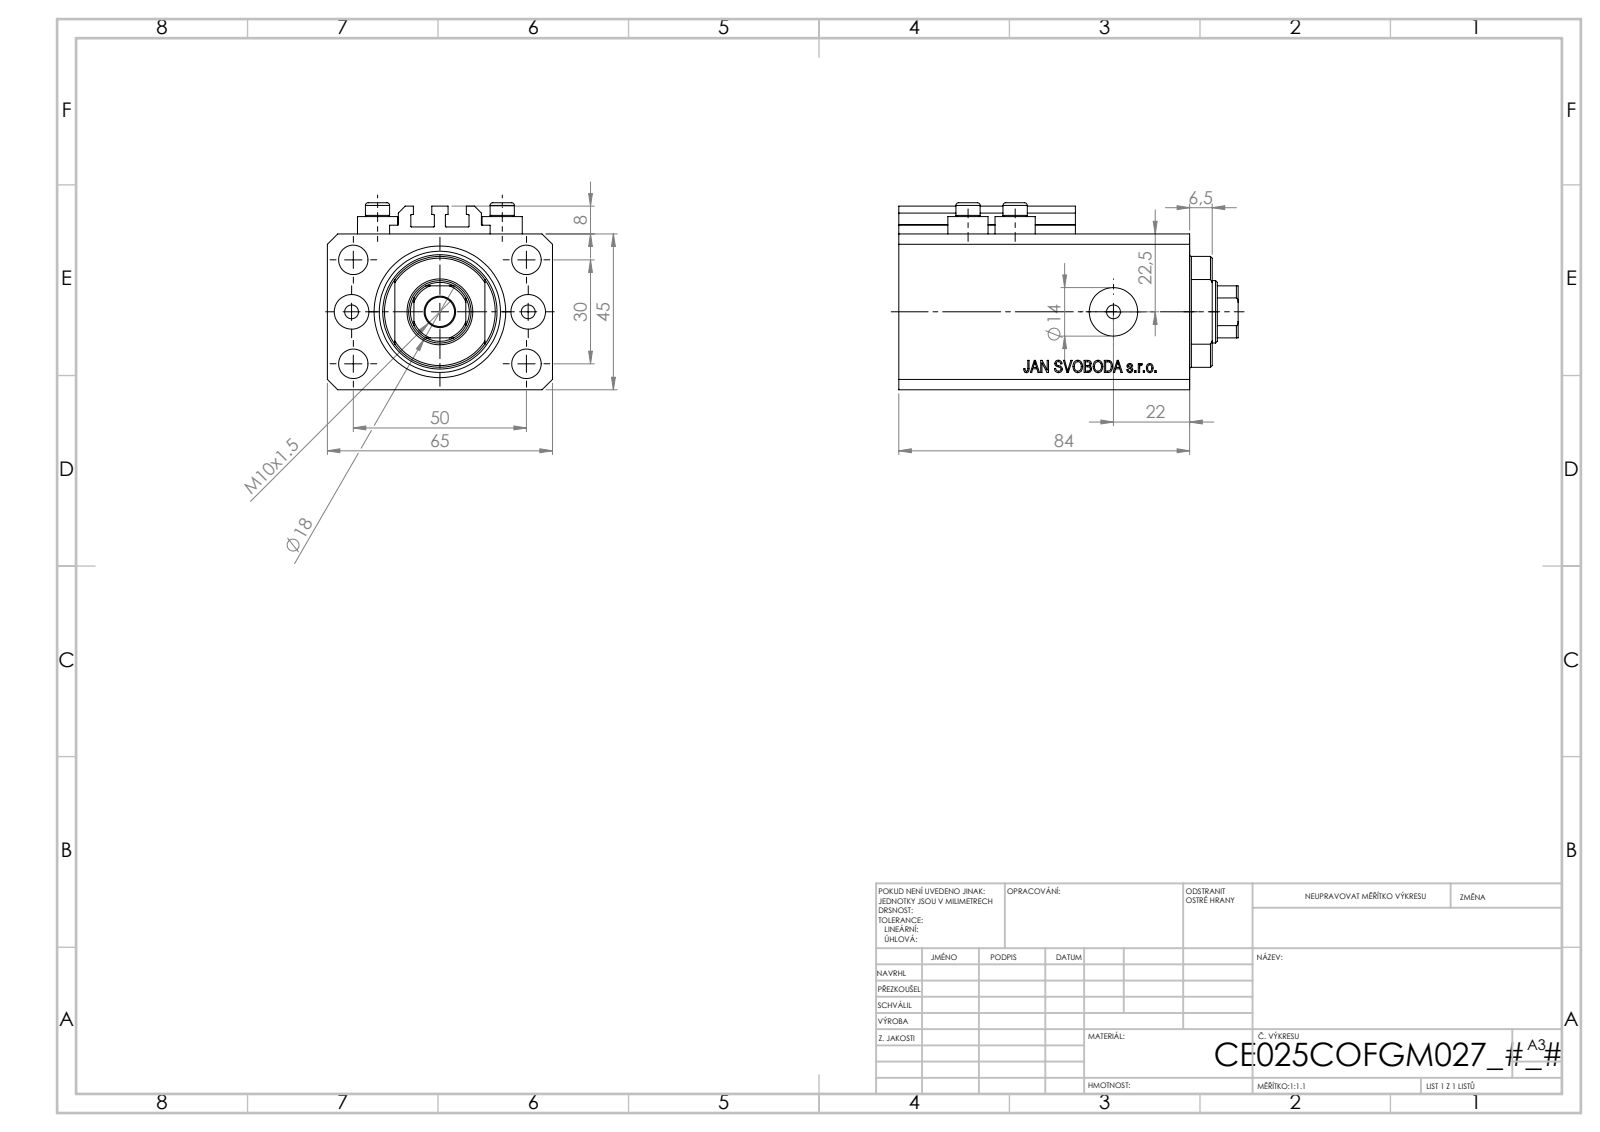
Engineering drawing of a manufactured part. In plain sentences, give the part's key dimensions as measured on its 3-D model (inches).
The part is named "V250CE_C_VCP; V250CE_VC_C; ALLEN BOLT V250CE; V250CE_C_Body". Its 3-D file was written by "SolidWorks 2019 (CONFIG_CONTROL_DESIGN)". It is 8 solids with 1034 faces: 504 planar, 86 cylindrical and 444 other. Overall it measures 3.858 by 2.559 by 2.126 inches. Its volume is 14.03 cubic inches and its surface area 94.79 square inches. Round holes: 8 of diameter 0.157, 5 of diameter 0.335, 2 of diameter 0.394, 2 of diameter 0.551, 1 of diameter 0.709, 1 of diameter 0.984, 1 of diameter 1.496. Round bosses or shafts: 4 of diameter 0.457, 4 of diameter 0.276. Partial cylindrical surfaces (rounded edges, fillets, slot ends): 10 of radius 0.008, 1 of radius 0.335, 1 of radius 0.63. The main face-to-face distances are 1.772, 2.559, 0.551, 2.756, 3.307, 1.85, 0.272, 2.484, 3.035, 0.118. The hole center spacings are 0.591, 1.148, 2.074, 0.535, 1.004, 1.181, 1.417, 1.515.
